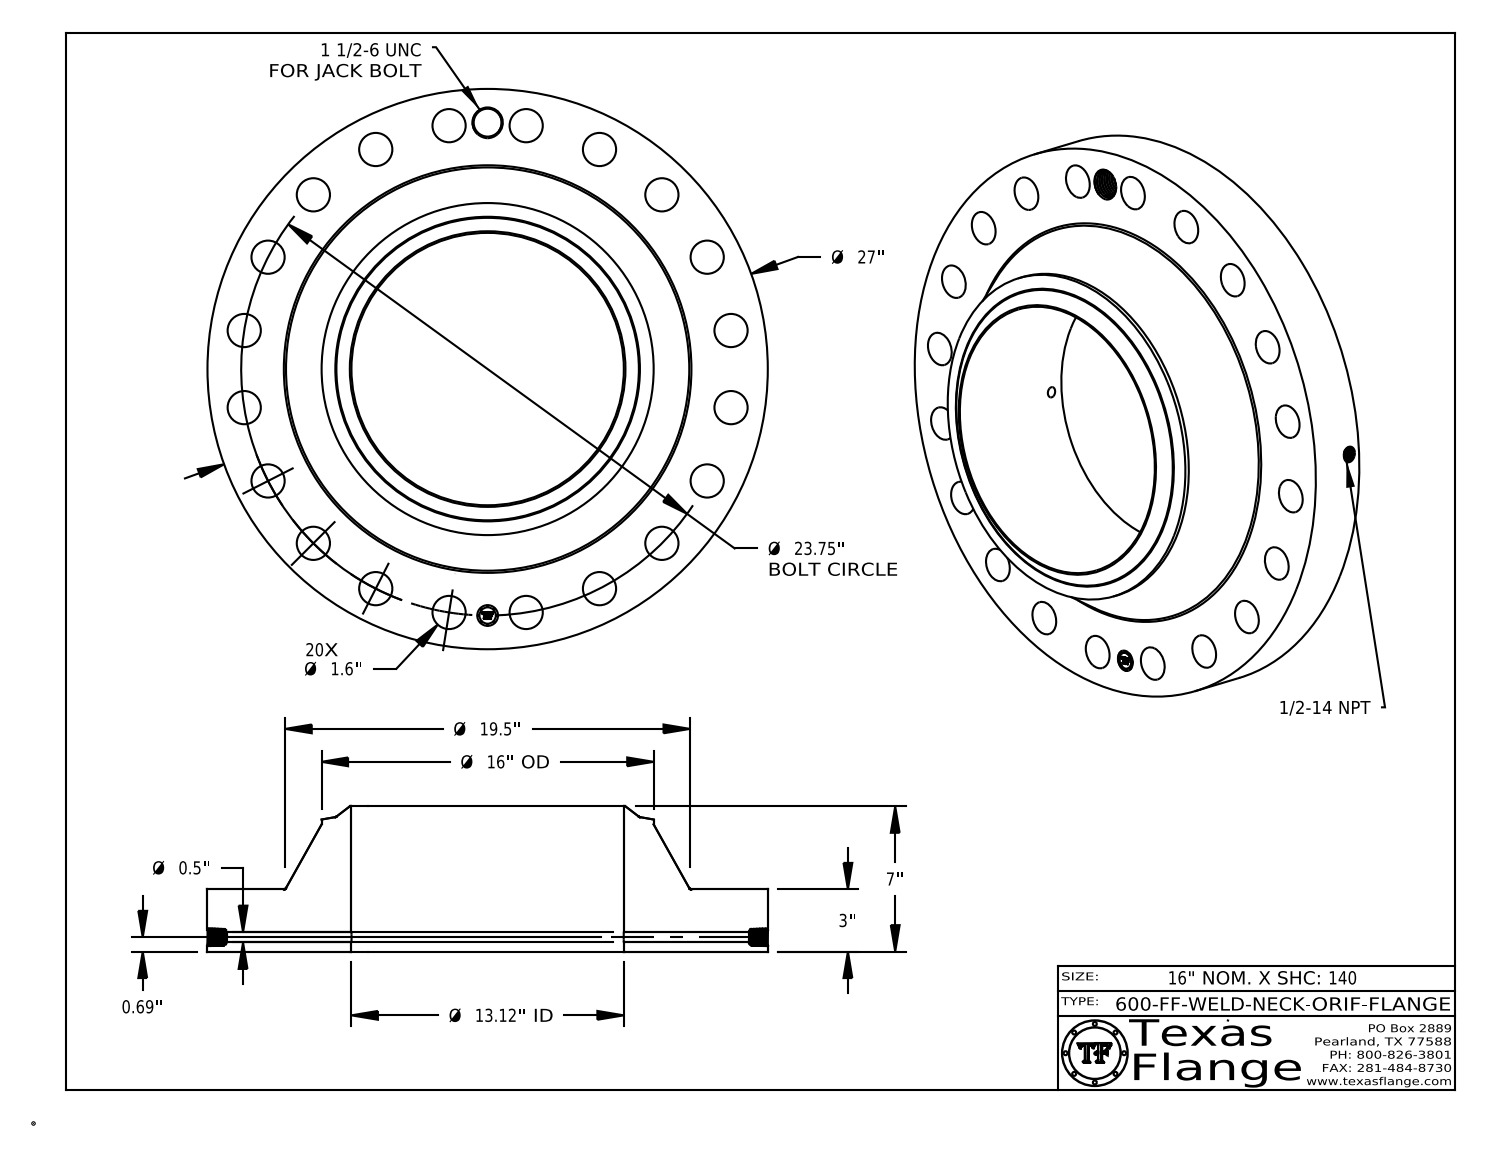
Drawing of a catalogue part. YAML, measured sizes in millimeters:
part_name: "600-FF-WELD-NECK"
step_written_by: "CATIA V5 STEP AP214 (AUTOMOTIVE_DESIGN)"
units: millimeters
bodies: {solids: 1, faces: 812, planar: 368, cylindrical: 122, other: 322}
overall_size: [685.8, 685.8, 177.8]
volume: 25680000
surface_area: 1162000
round_holes:
  - {diameter: 40.6, count: 20}
  - {diameter: 12.7, count: 1}
  - {diameter: 17.1, count: 1}
  - {diameter: 25.4, count: 1}
  - {diameter: 34.1, count: 1}
  - {diameter: 333.3, count: 1}
round_bosses_or_shafts:
  - {diameter: 1.5, count: 8}
  - {diameter: 685.8, count: 1}
  - {diameter: 406.4, count: 1}
  - {diameter: 20, count: 1}
face_to_face_distances: [76.2, 177.8, 101.6, 0.4, 75.8, 102, 7.6, 7.4, 1.4, 6.3]
hole_center_spacings: [301.6, 426.6, 573.7, 595.8, 94.4, 354.6, 488, 186.4]
